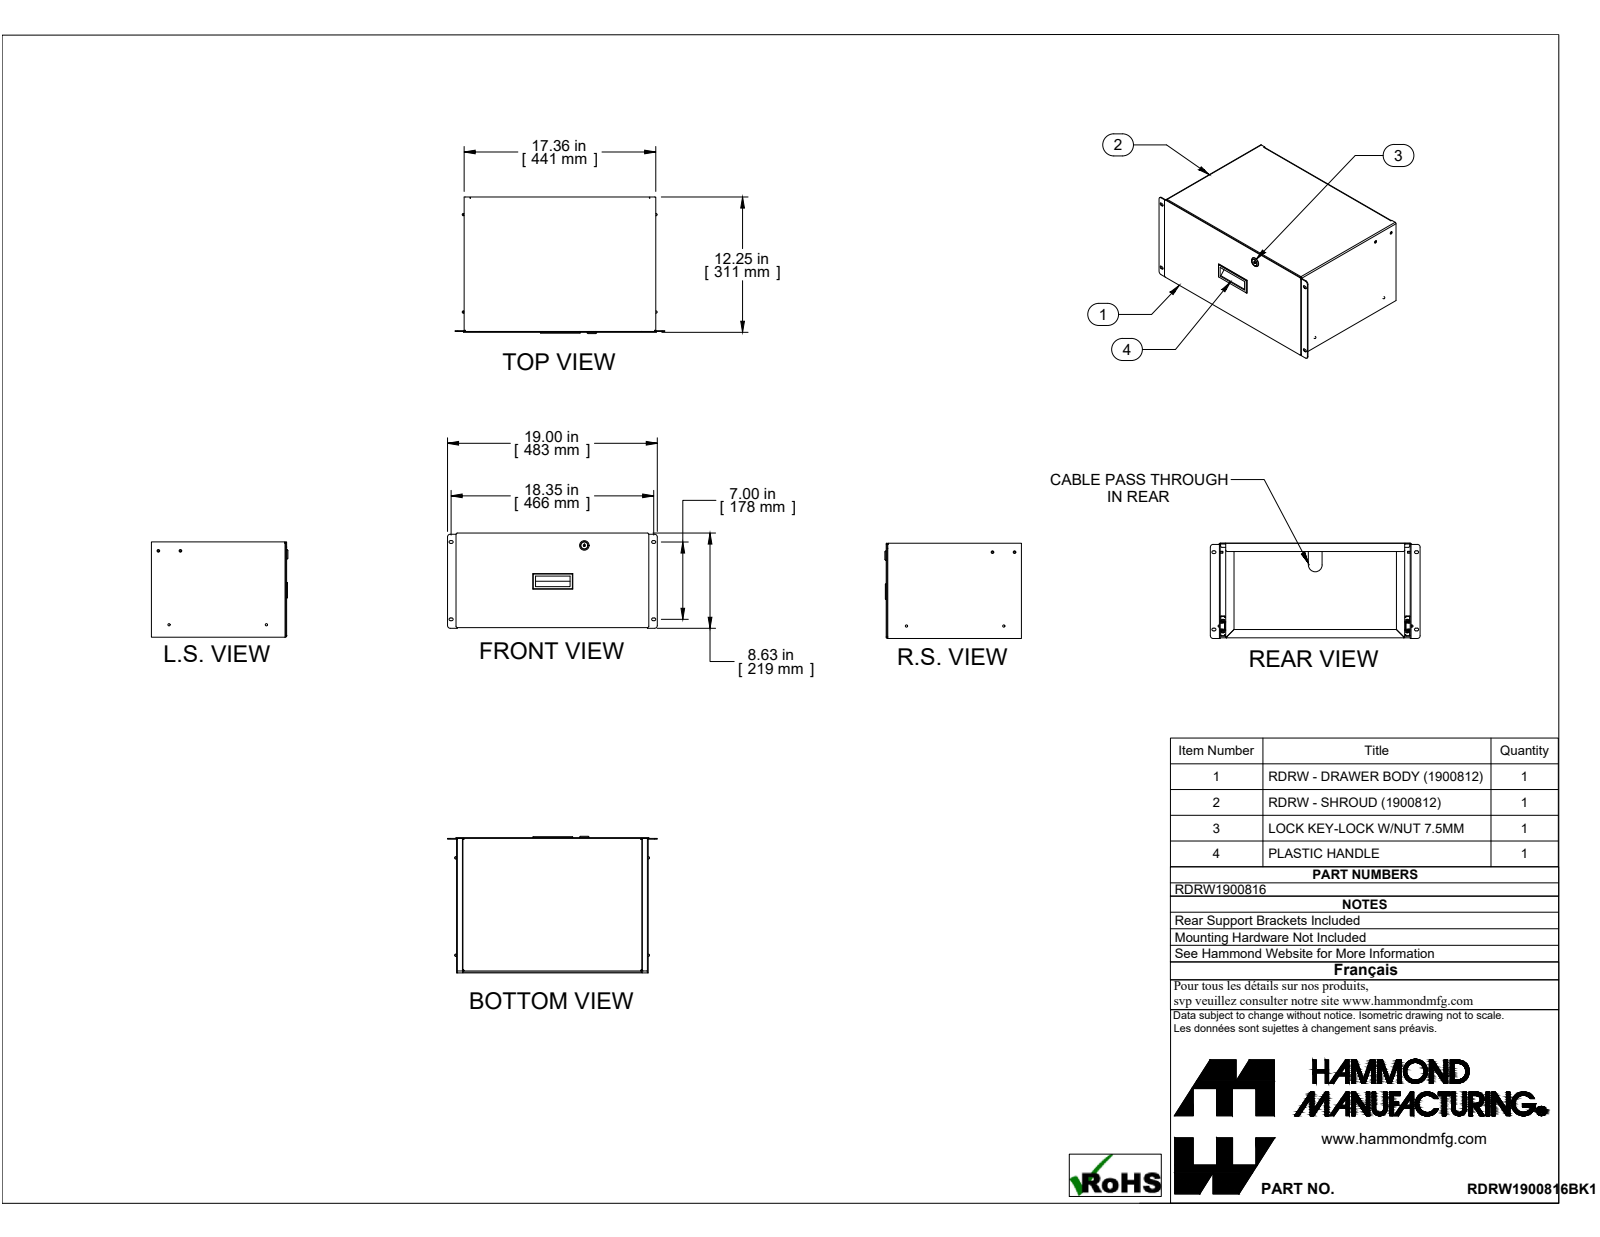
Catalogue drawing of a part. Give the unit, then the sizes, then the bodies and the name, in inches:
Units: inches
Overall size (bounding box): 19 × 16.395 × 8.626
Round holes (diameter × count): ⌀0.177 ×6, ⌀0.156 ×4, ⌀0.18 ×4, ⌀0.25 ×4, ⌀0.172 ×3, ⌀0.163 ×2, ⌀0.153 ×1, ⌀0.198 ×1, ⌀0.625 ×1
Round bosses / shafts (diameter × count): ⌀0.235 ×2, ⌀0.164 ×2, ⌀0.866 ×1, ⌀0.547 ×1, ⌀0.335 ×1
Partial cylindrical surfaces — rounded edges, fillets, slot ends (radius × count): R0.086 ×52, R0.029 ×40, R0.05 ×16, R0.125 ×16, R0.024 ×8, R0.072 ×8, R0.036 ×6, R0.1 ×6
Main face-to-face distances: 0.072, 0.048, 16.712, 0.5, 0.572, 16.784, 17.284, 8.491, 8.563, 8.443
Hole centre spacings: 0.38, 12.6, 0.36, 0.622, 0.74, 1.002, 1.26, 1.362
Volume: 97.1 in³ · Surface area: 3 252 in²
Bodies: 24 solids, 682 faces (376 planar, 264 cylindrical, 42 other)
Part name (STEP PRODUCT): RDRW1900816BK1
STEP written by: SolidWorks 2019 (CONFIG_CONTROL_DESIGN)
